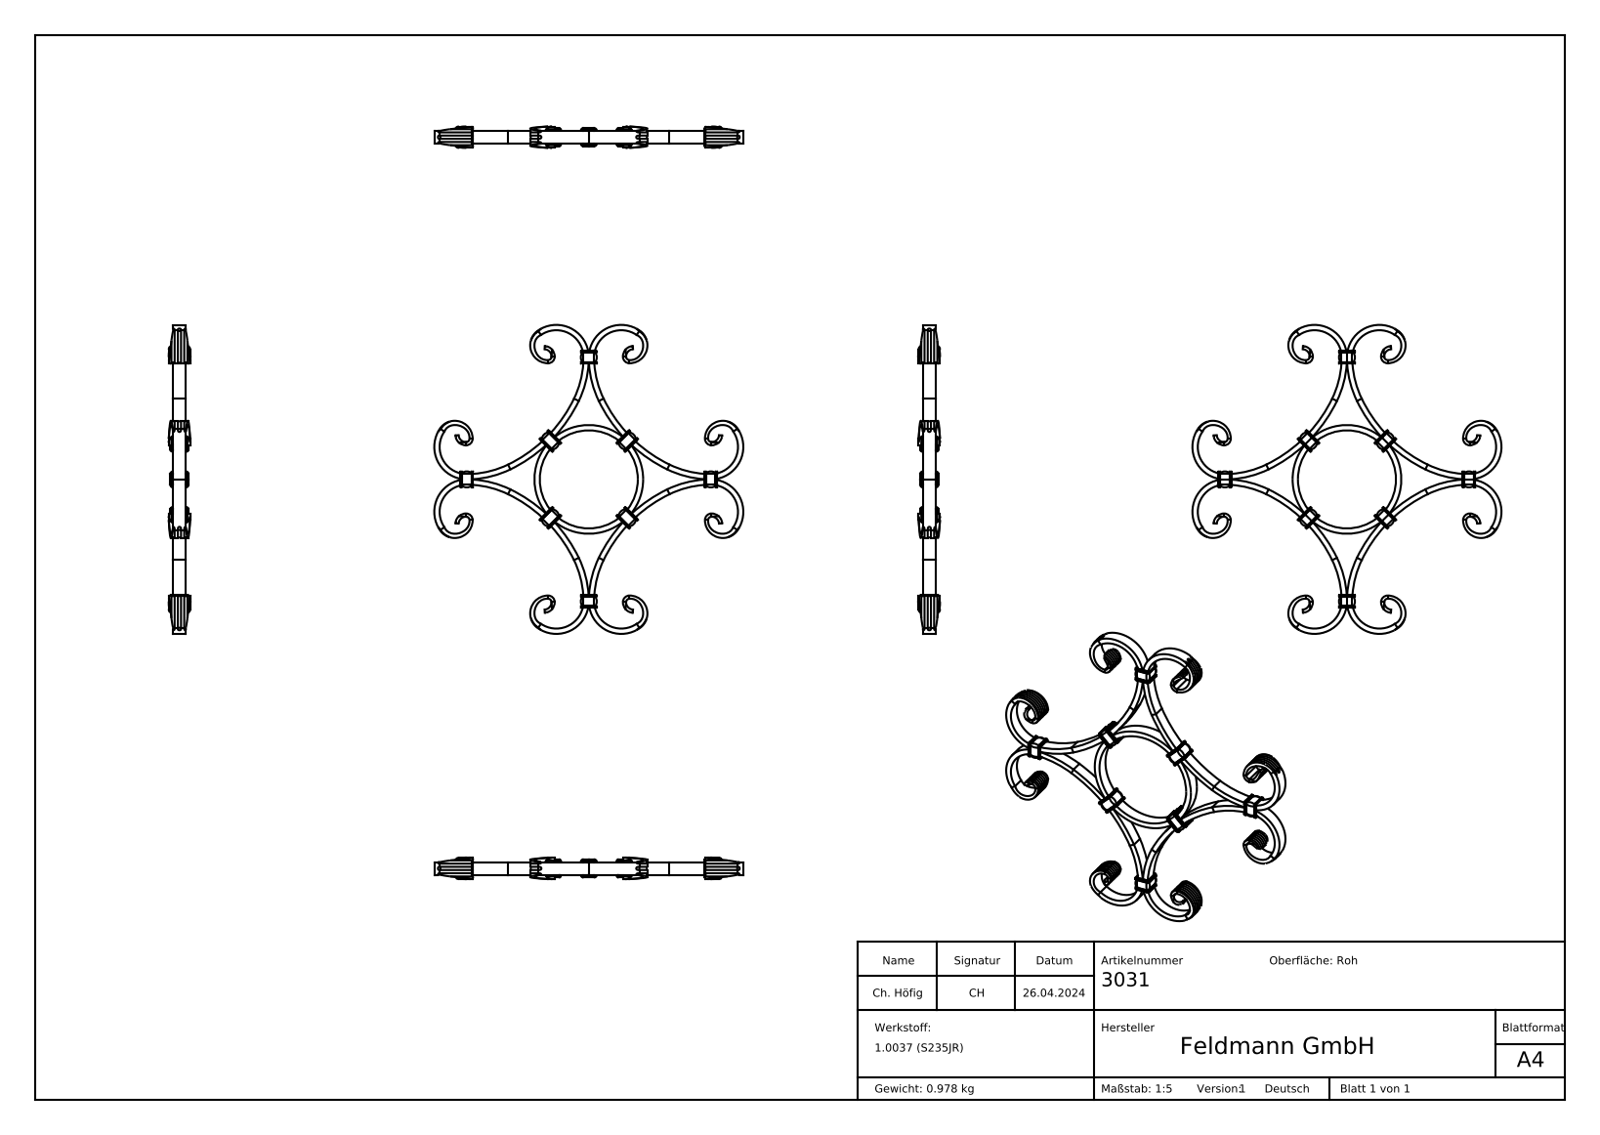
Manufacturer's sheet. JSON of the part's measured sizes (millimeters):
{"part_name": "3031", "step_written_by": "SolidWorks 2018 (CONFIG_CONTROL_DESIGN)", "units": "millimeters", "bodies": {"solids": 13, "faces": 1659, "planar": 572, "cylindrical": 562, "other": 525}, "overall_size": [290, 290, 20], "volume_mm3": 125343, "surface_area_mm2": 83699, "round_holes": [[92, 1]], "round_bosses_or_shafts": [[102, 1]], "partial_cylinders_radius": [[0.5, 200], [0.1, 64], [7.5, 28], [2.5, 24], [7, 24], [3.2, 8], [6.2, 8], [10, 8]], "face_to_face_distances": [12, 50.99, 1.5, 10.5, 101.98, 4, 16, 38.99, 10, 62.99]}
